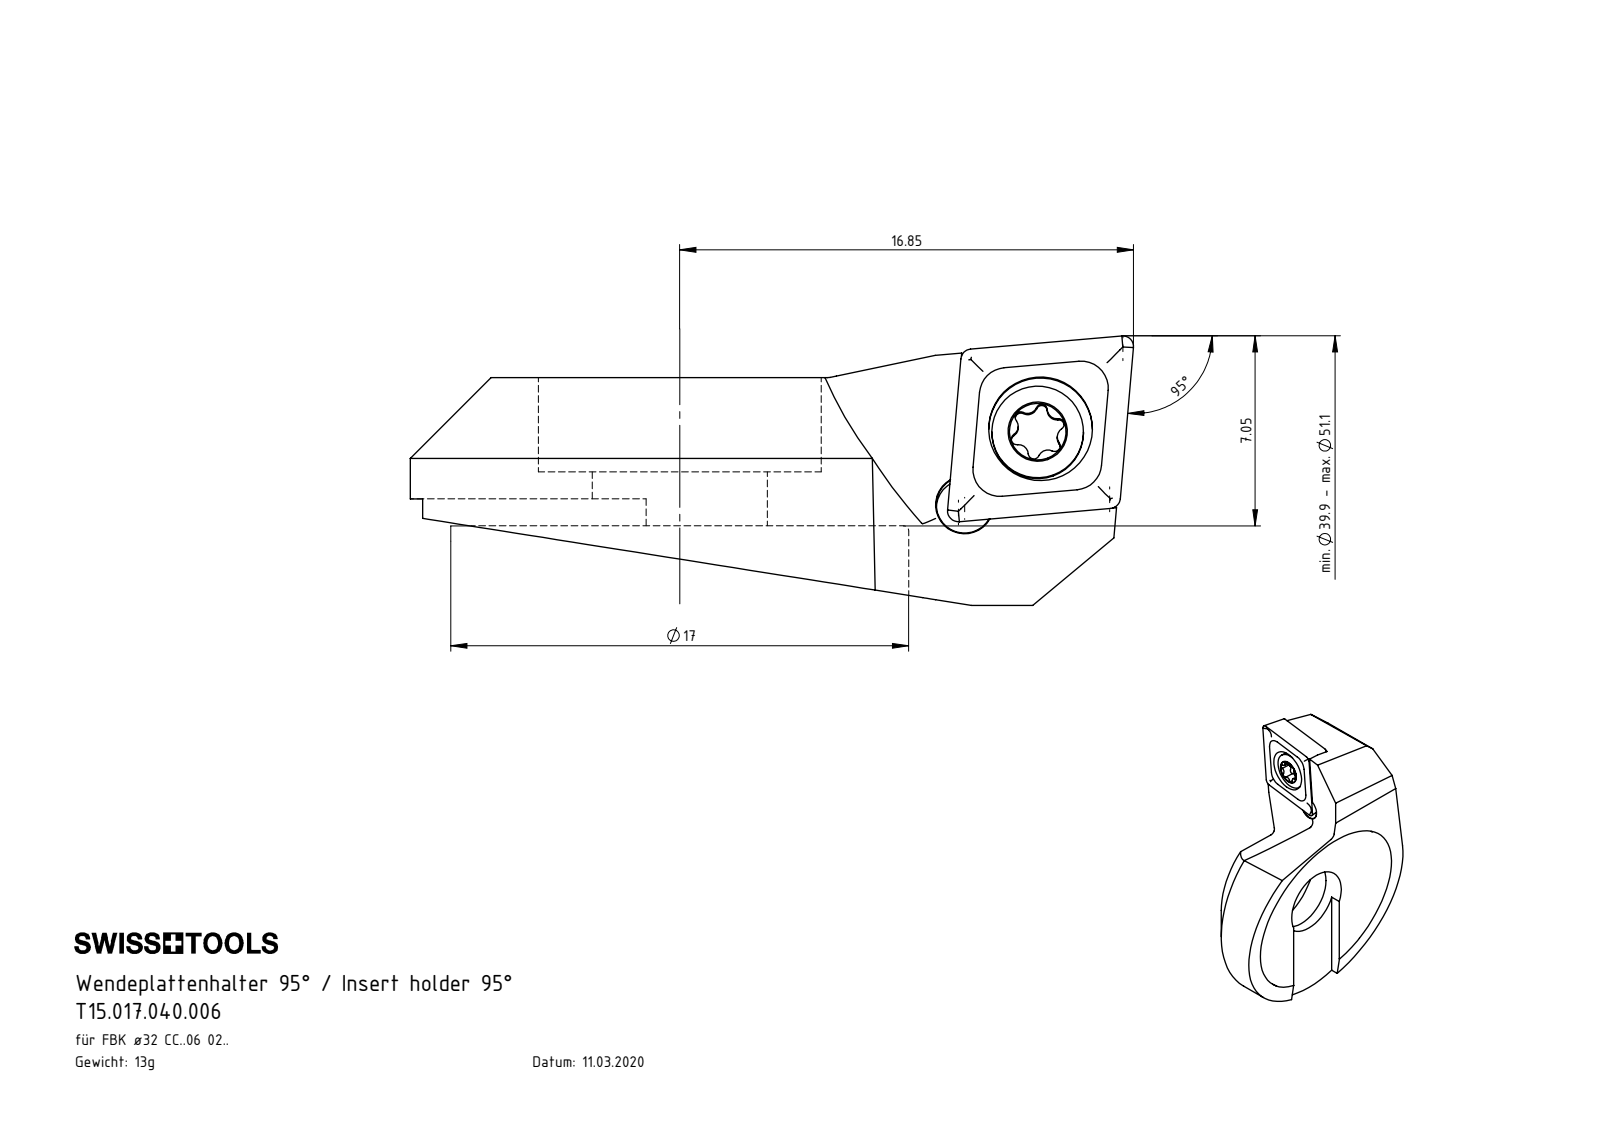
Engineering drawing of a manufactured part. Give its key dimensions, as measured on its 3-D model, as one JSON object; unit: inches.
{"part_name": "WCA-ER2.001.006_A; F32.WCA.002.007; F32-WCA.002.007_B_fertigbearbeitet; CCMT060204", "step_written_by": "SolidWorks 2017 (AUTOMOTIVE_DESIGN)", "units": "inches", "bodies": {"solids": 3, "faces": 103, "planar": 39, "cylindrical": 26, "other": 38}, "overall_size": [1.057, 0.787, 0.394], "volume_in3": 0.095, "surface_area_in2": 2.387, "round_holes": [[0.081, 1], [0.083, 1], [0.11, 1], [0.152, 1], [0.256, 1], [0.413, 1]], "round_bosses_or_shafts": [[0.134, 1], [0.098, 1]], "partial_cylinders_radius": [[0.008, 6], [0.014, 5], [0.02, 2], [0.014, 1], [0.197, 1], [0.335, 1], [0.394, 1], [0.591, 1]], "face_to_face_distances": [0.039, 0.217, 0.138, 0.079, 0.177, 0.09, 0.333, 0.195, 0.156, 0.116], "hole_center_spacings": [0.151, 0.157]}
